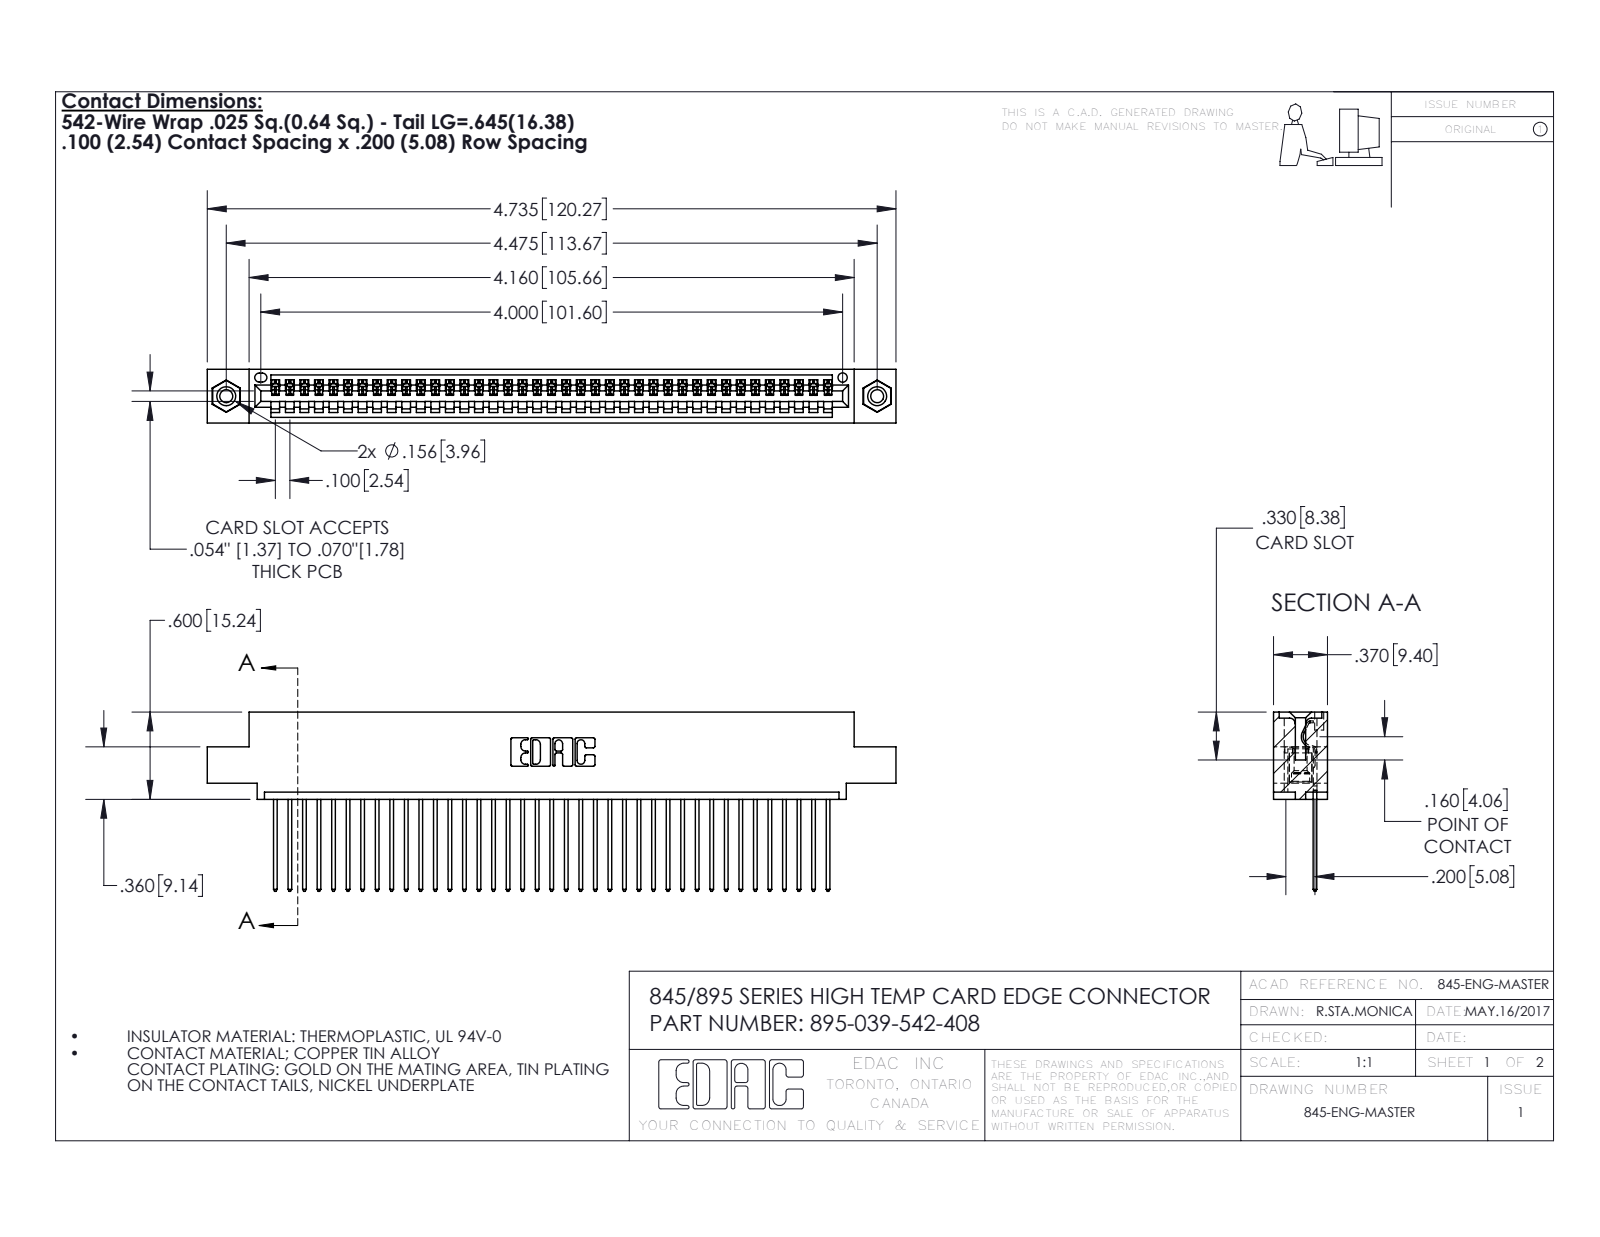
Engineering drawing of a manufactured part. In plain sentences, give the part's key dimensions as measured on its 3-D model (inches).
The part is named "395-039-542-408; 345-250-001_345-250-003-102; 345-292-001_345-293-142; 345 Part_0.110 Offset - 0.156 Dia-TI". Its 3-D file was written by "SolidWorks 2016 (CONFIG_CONTROL_DESIGN)". It is 42 solids with 2452 faces: 1676 planar, 760 cylindrical and 16 other. Overall it measures 4.735 by 1.232 by 0.37 inches. Its volume is 0.696 cubic inches and its surface area 24.44 square inches. Round holes: 2 of diameter 0.089, 2 of diameter 0.125, 2 of diameter 0.156, 1 of diameter 0.064. Round bosses or shafts: 2 of diameter 0.155. Partial cylindrical surfaces (rounded edges, fillets, slot ends): 78 of radius 0.006, 78 of radius 0.01, 22 of radius 0.01, 6 of radius 0.007, 6 of radius 0.031, 3 of radius 0.026, 2 of radius 0.031, 2 of radius 0.04. The main face-to-face distances are 0.072, 0.298, 0.37, 0.098, 0.272, 0.025, 0.2, 0.225, 0.149, 0.072. The hole center spacings are 0.27, 4.239, 4.475.
